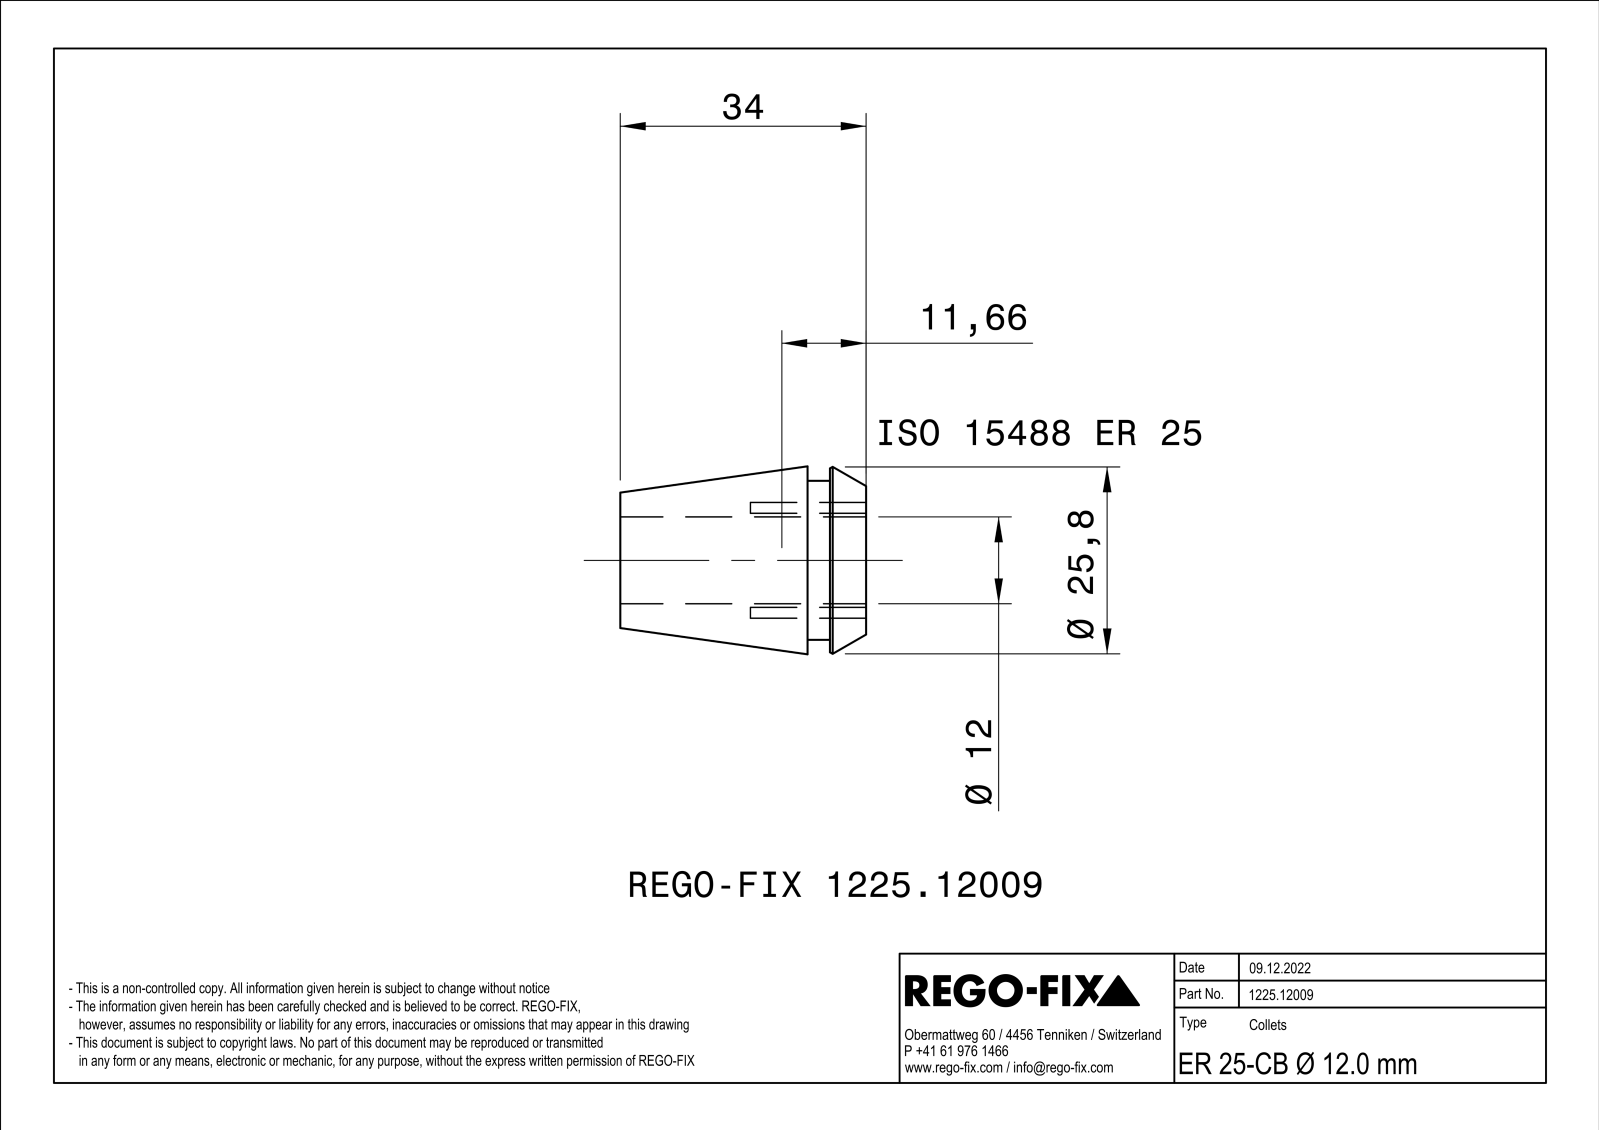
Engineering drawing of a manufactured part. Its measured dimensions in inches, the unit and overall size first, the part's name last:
Units: inches
Overall size (bounding box): 1.339 × 1.023 × 1.023
Round holes (diameter × count): ⌀0.059 ×4, ⌀0.472 ×1
Round bosses / shafts (diameter × count): ⌀1.024 ×1, ⌀0.866 ×1
Main face-to-face distances: 0.031, 0.197, 1.339, 1.142, 0.319, 0.122, 1.02
Hole centre spacings: 0.285, 0.404, 0.571
Volume: 0.49 in³ · Surface area: 12.45 in²
Bodies: 1 solid, 178 faces (64 planar, 21 cylindrical, 93 other)
Part name (STEP PRODUCT): NOCUT
STEP written by: SIEMENS PLM Software Solid Edge ST10 (AUTOMOTIVE_DESIGN)
